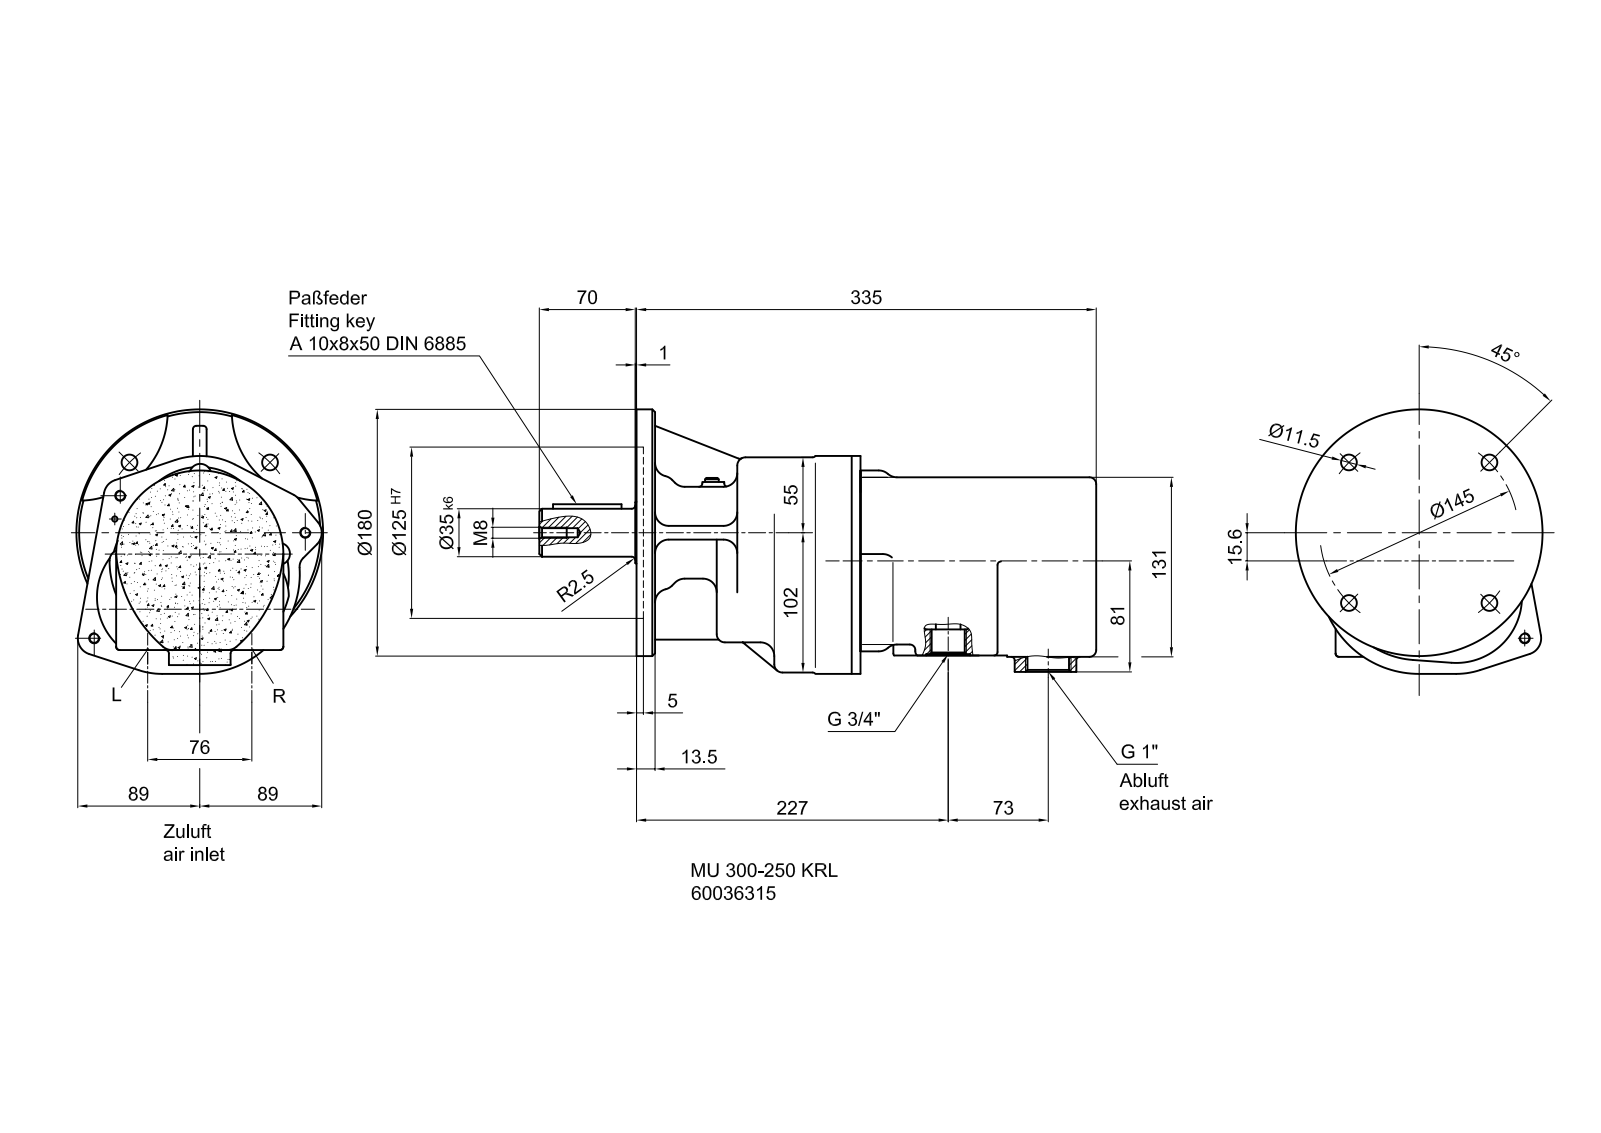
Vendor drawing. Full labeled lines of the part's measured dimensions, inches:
Part name (STEP PRODUCT): MU 300-250 KRL_60036315
STEP written by: Autodesk Inventor 2018 (CONFIG_CONTROL_DESIGN)
Units: inches
Bodies: 2 solids, 937 faces (331 planar, 323 cylindrical, 283 other)
Overall size (bounding box): 16.012 × 7.598 × 7.087
Volume: 279.1 in³ · Surface area: 469.6 in²
Round holes (diameter × count): ⌀0.194 ×4, ⌀0.262 ×4, ⌀0.453 ×4, ⌀0.335 ×3, ⌀0.374 ×3, ⌀0.256 ×2, ⌀0.95 ×2, ⌀1.26 ×2, ⌀0.098 ×1, ⌀0.11 ×1, ⌀0.154 ×1, ⌀0.157 ×1
Round bosses / shafts (diameter × count): ⌀0.583 ×3, ⌀0.512 ×3, ⌀0.315 ×3, ⌀7.087 ×1, ⌀4.803 ×1, ⌀1.772 ×1, ⌀1.378 ×1, ⌀0.63 ×1
Partial cylindrical surfaces — rounded edges, fillets, slot ends (radius × count): R0.079 ×30, R0.098 ×29, R0.157 ×20, R0.118 ×12, R0.236 ×12, R0.394 ×12, R0.039 ×6, R0.059 ×6
Main face-to-face distances: 0.197, 0.039, 13.224, 0.295, 13.028, 6.772, 6.256, 6.453, 12.693, 5.921
Hole centre spacings: 1.181, 2.855, 3.217, 4.037, 2.258, 2.992, 5.439, 1.083
